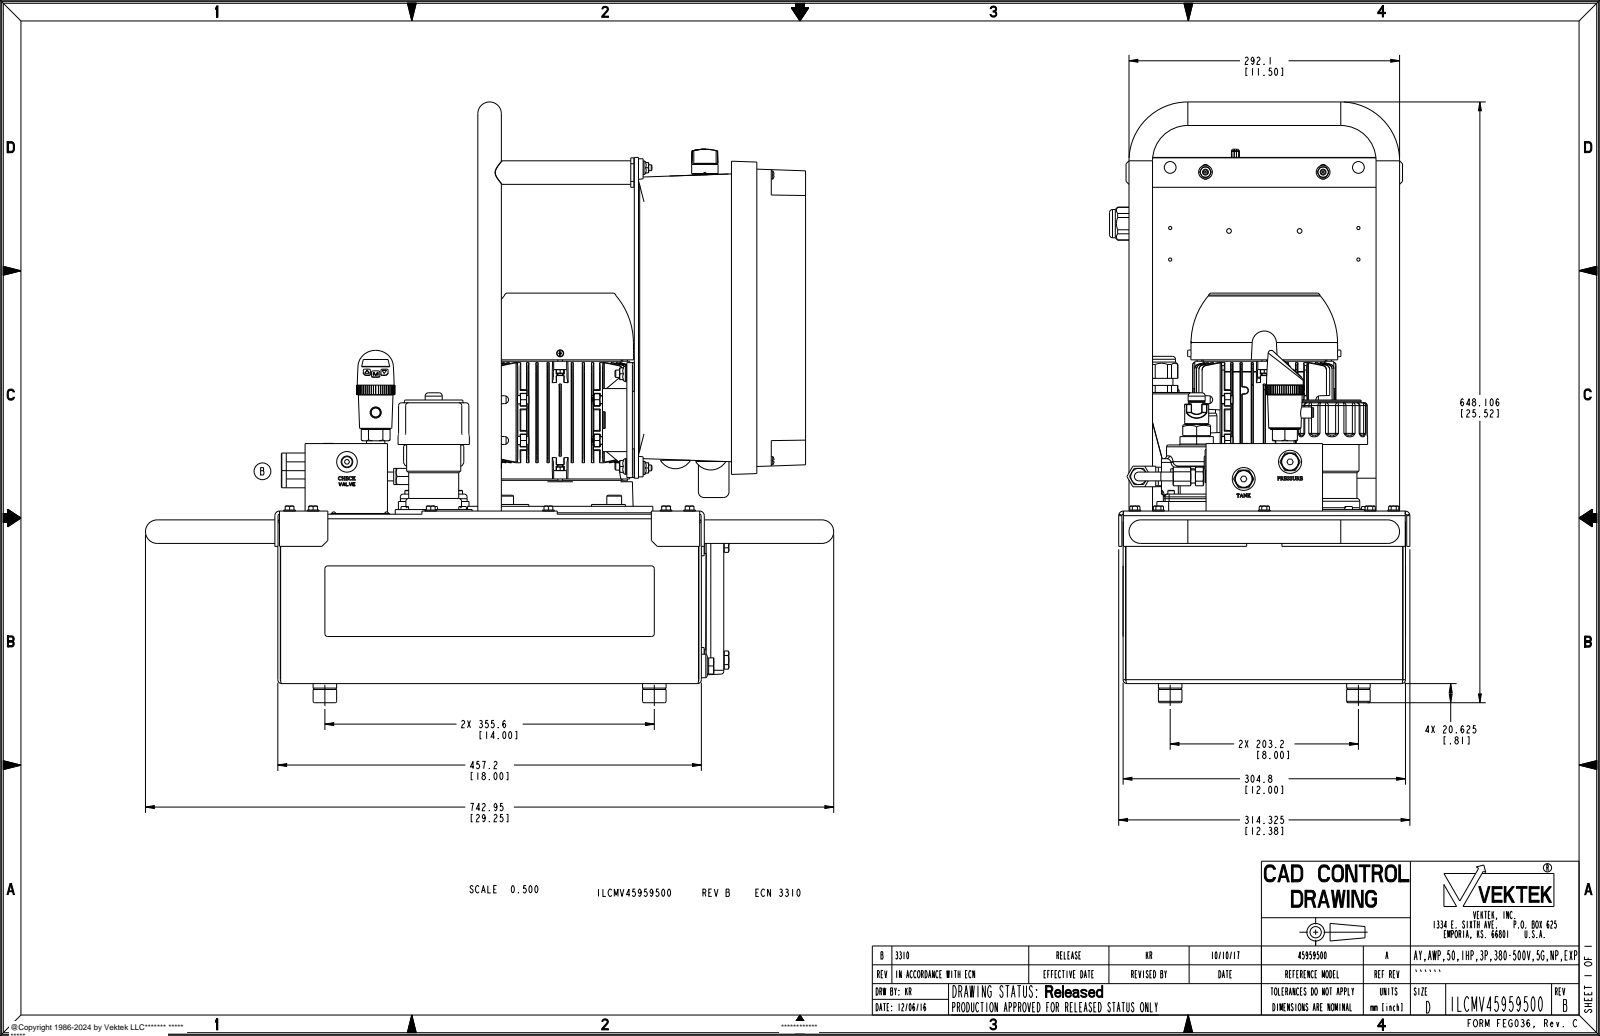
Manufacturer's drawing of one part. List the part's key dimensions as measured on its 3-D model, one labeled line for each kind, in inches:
Part name (STEP PRODUCT): ILCMV45959500
STEP written by: PRO/ENGINEER BY PARAMETRIC TECHNOLOGY CORPORATION, 2013320 (AUTOMOTIVE_DESIGN)
Units: inches
Bodies: 20 solids, 10008 faces (4898 planar, 2411 cylindrical, 2699 other)
Overall size (bounding box): 29.25 × 25.516 × 12.764
Volume: 648.1 in³ · Surface area: 5 146 in²
Round holes (diameter × count): ⌀0.312 ×14, ⌀0.344 ×14, ⌀0.375 ×14, ⌀0.136 ×13, ⌀0.236 ×11, ⌀0.75 ×9, ⌀0.118 ×8, ⌀0.472 ×8, ⌀0.217 ×6, ⌀0.218 ×6, ⌀0.236 ×6, ⌀0.354 ×6
Round bosses / shafts (diameter × count): ⌀0.25 ×24, ⌀1 ×14, ⌀0.5 ×14, ⌀0.197 ×14, ⌀0.375 ×9, ⌀0.35 ×8, ⌀0.177 ×8, ⌀0.584 ×6
Partial cylindrical surfaces — rounded edges, fillets, slot ends (radius × count): R0.02 ×82, R0.079 ×61, R0.005 ×54, R0.039 ×53, R0.118 ×42, R0.157 ×28, R0.108 ×18, R0.06 ×14
Main face-to-face distances: 0.105, 0.138, 11.895, 17.895, 7.28, 7.06, 6.955, 0.108, 7.172, 11.79
Hole centre spacings: 0.098, 8, 0.139, 0.566, 2.342, 2.756, 3.248, 3.897
